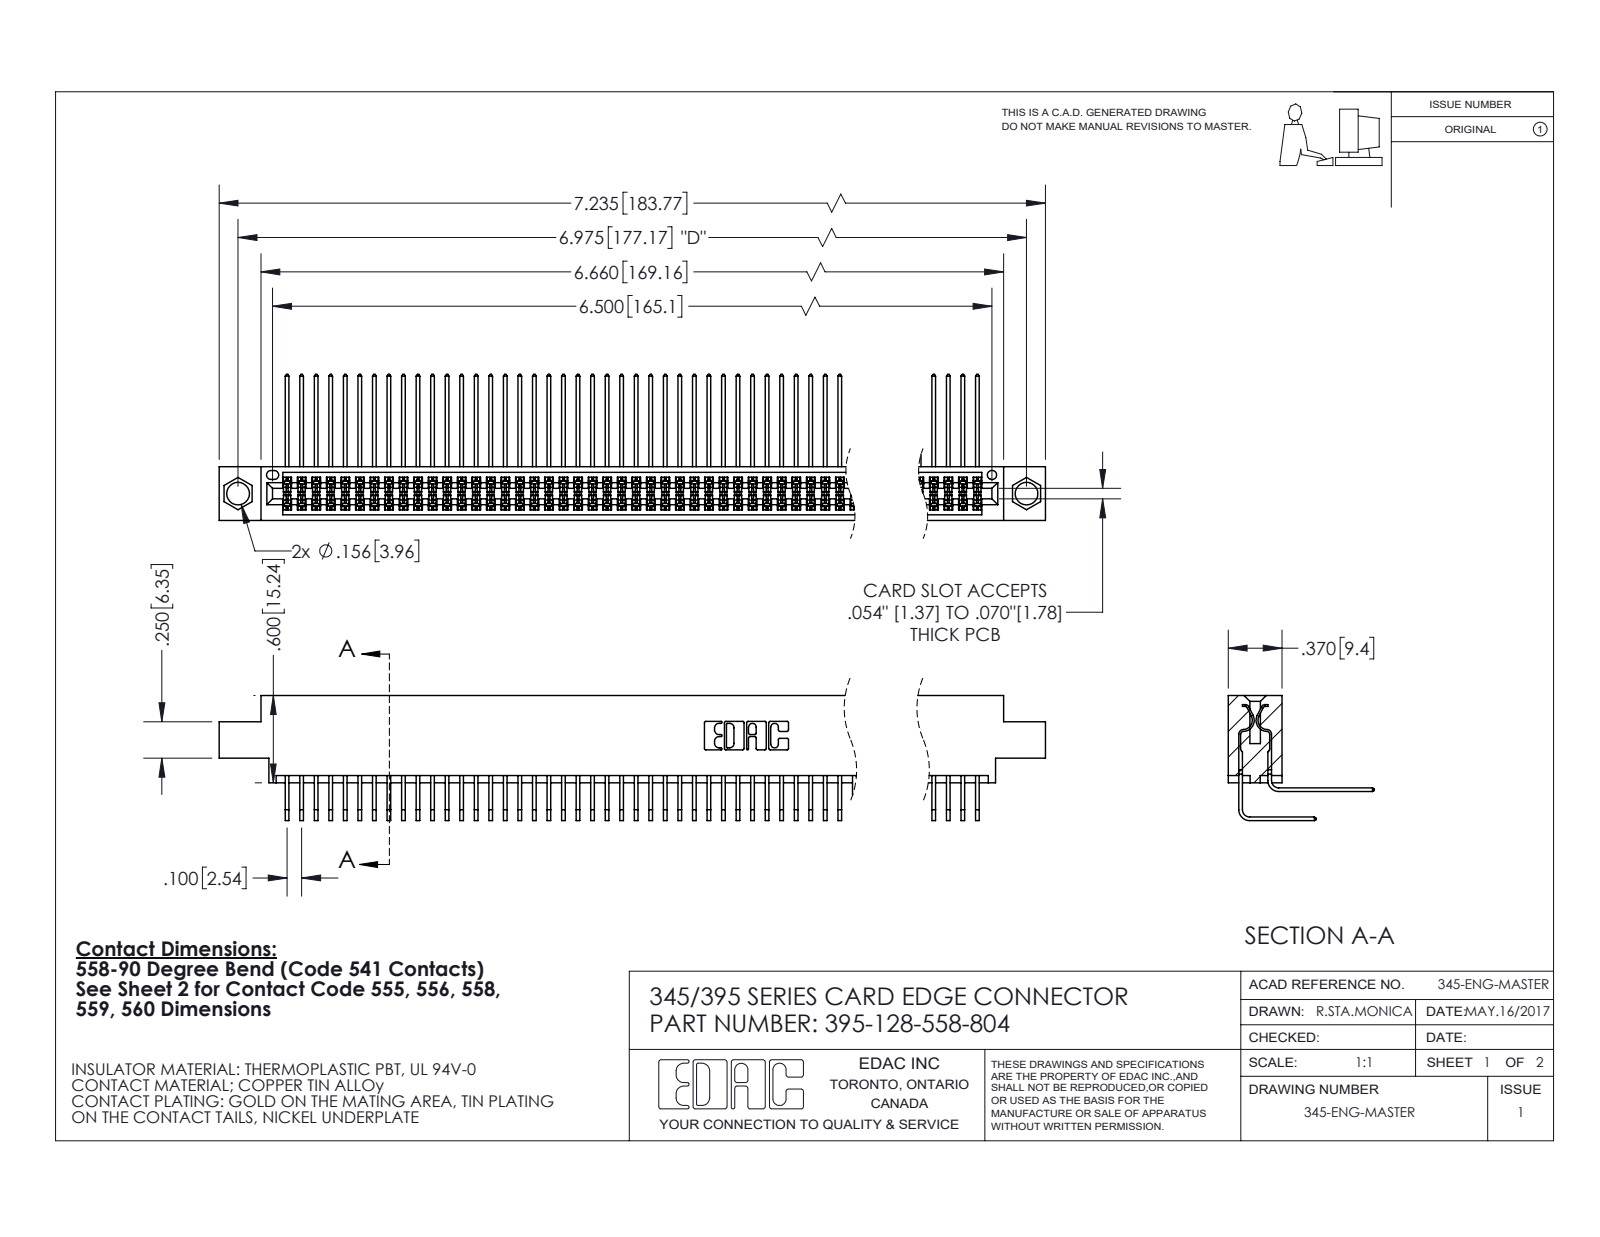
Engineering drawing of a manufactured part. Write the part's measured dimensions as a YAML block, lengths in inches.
part_name: "345 Part_0.170 Offset - 0.156 Dia-TI; 345-292-001_558 Tail - 2; 395-128-558-804; 345-292-001_558 559 Tail - 1"
step_written_by: "SolidWorks 2020 (CONFIG_CONTROL_DESIGN)"
units: inches
bodies: {solids: 129, faces: 6800, planar: 4578, cylindrical: 2222, other: 0}
overall_size: [7.235, 1.005, 0.859]
volume: 1.134
surface_area: 48.59
round_holes:
  - {diameter: 0.156, count: 2}
  - {diameter: 0.064, count: 1}
partial_cylinders:
  - {radius: 0.006, count: 192}
  - {radius: 0.01, count: 22}
  - {radius: 0.007, count: 6}
  - {radius: 0.031, count: 6}
  - {radius: 0.026, count: 3}
  - {radius: 0.014, count: 2}
  - {radius: 0.019, count: 2}
  - {radius: 0.022, count: 2}
face_to_face_distances: [0.072, 0.298, 0.2, 0.37, 0.098, 0.272, 0.025, 0.225, 0.175, 0.025]
hole_center_spacings: [0.27, 6.739, 6.975]
